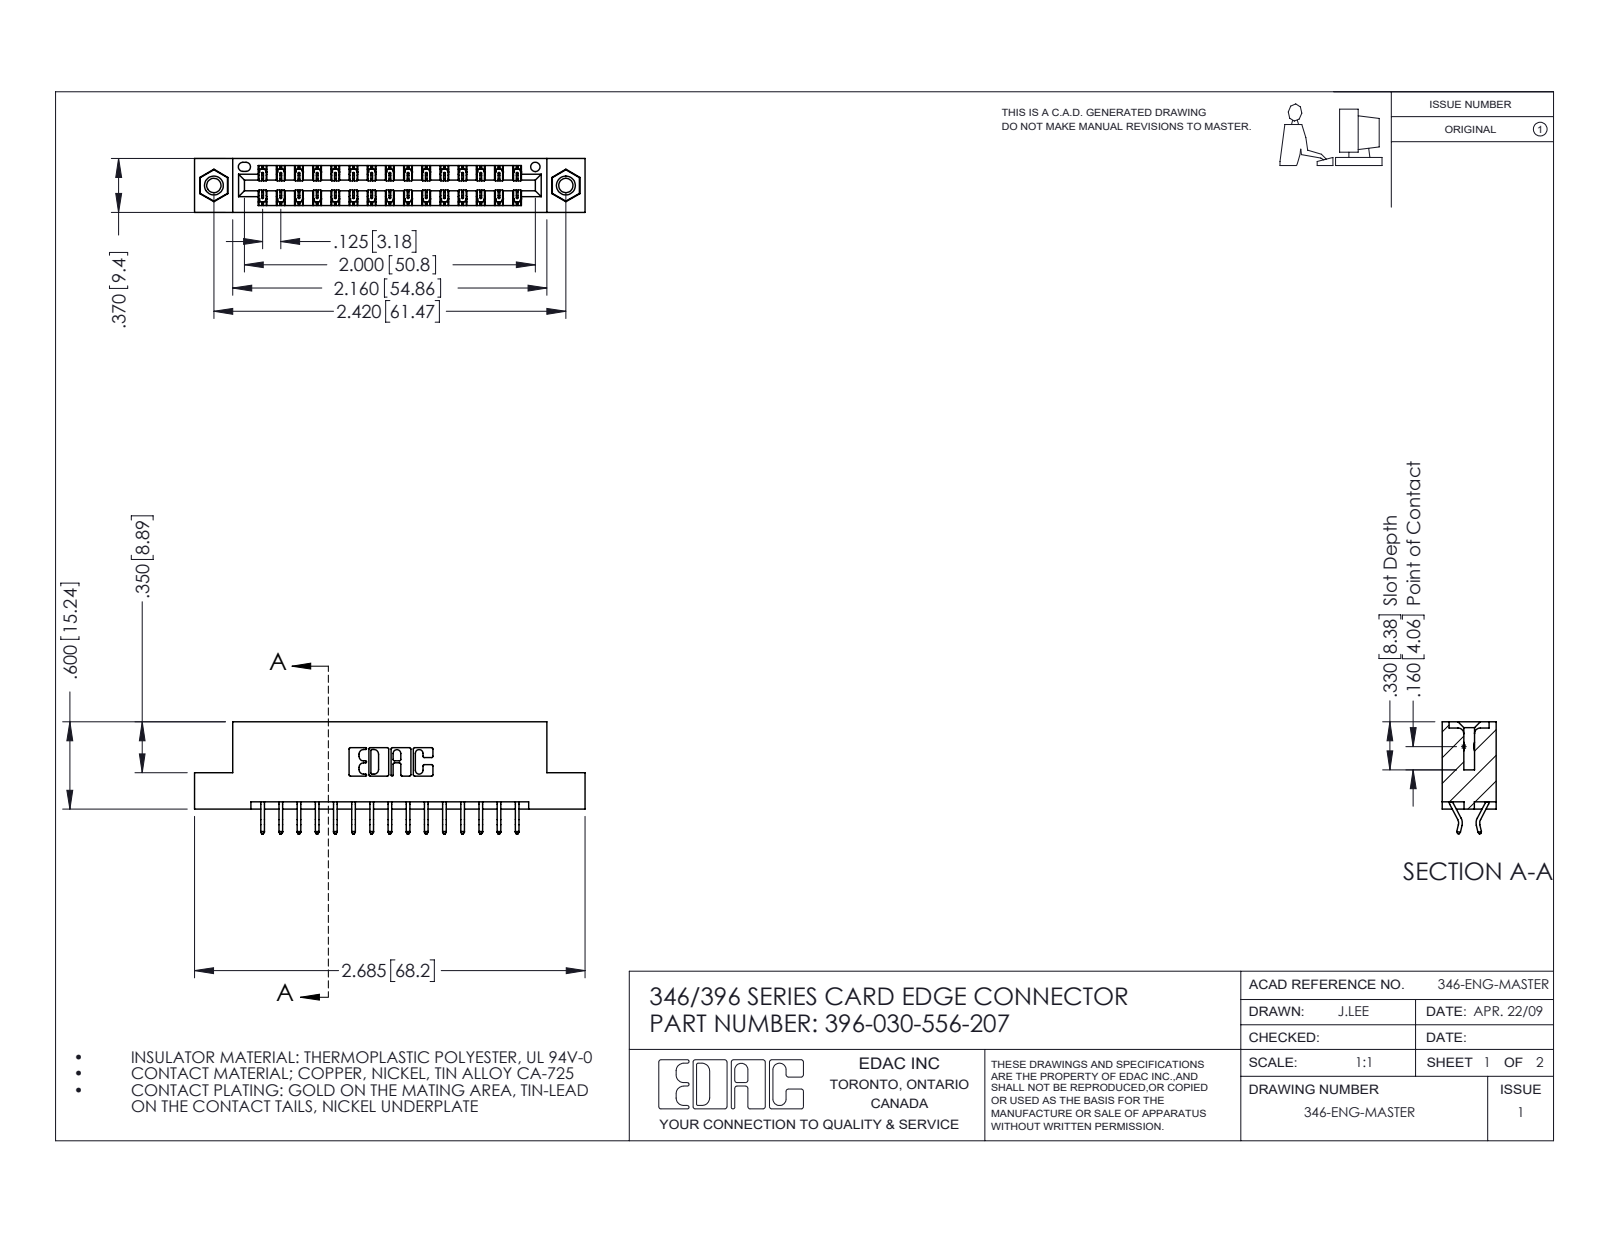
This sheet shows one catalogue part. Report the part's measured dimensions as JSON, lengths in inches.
{"part_name": "345-250-001_345-250-005-103; 345-292-001_556 Tail; 346 Part_Flush Mounting Lugs - 0.156 Dia-TI; 396-030-556-207", "step_written_by": "SolidWorks 2016 (CONFIG_CONTROL_DESIGN)", "units": "inches", "bodies": {"solids": 33, "faces": 1922, "planar": 1278, "cylindrical": 628, "other": 16}, "overall_size": [2.685, 0.77, 0.37], "volume_in3": 0.392, "surface_area_in2": 13.04, "round_holes": [[0.098, 2], [0.125, 2], [0.156, 2], [0.064, 1]], "round_bosses_or_shafts": [[0.155, 2]], "partial_cylinders_radius": [[0.006, 45], [0.01, 22], [0.007, 6], [0.031, 6], [0.026, 3], [0.01, 2], [0.014, 2], [0.022, 2]], "face_to_face_distances": [0.048, 0.322, 0.25, 0.37, 0.025, 0.072, 0.298, 0.275, 0.148, 0.222], "hole_center_spacings": [0.246, 2.213, 2.42]}
